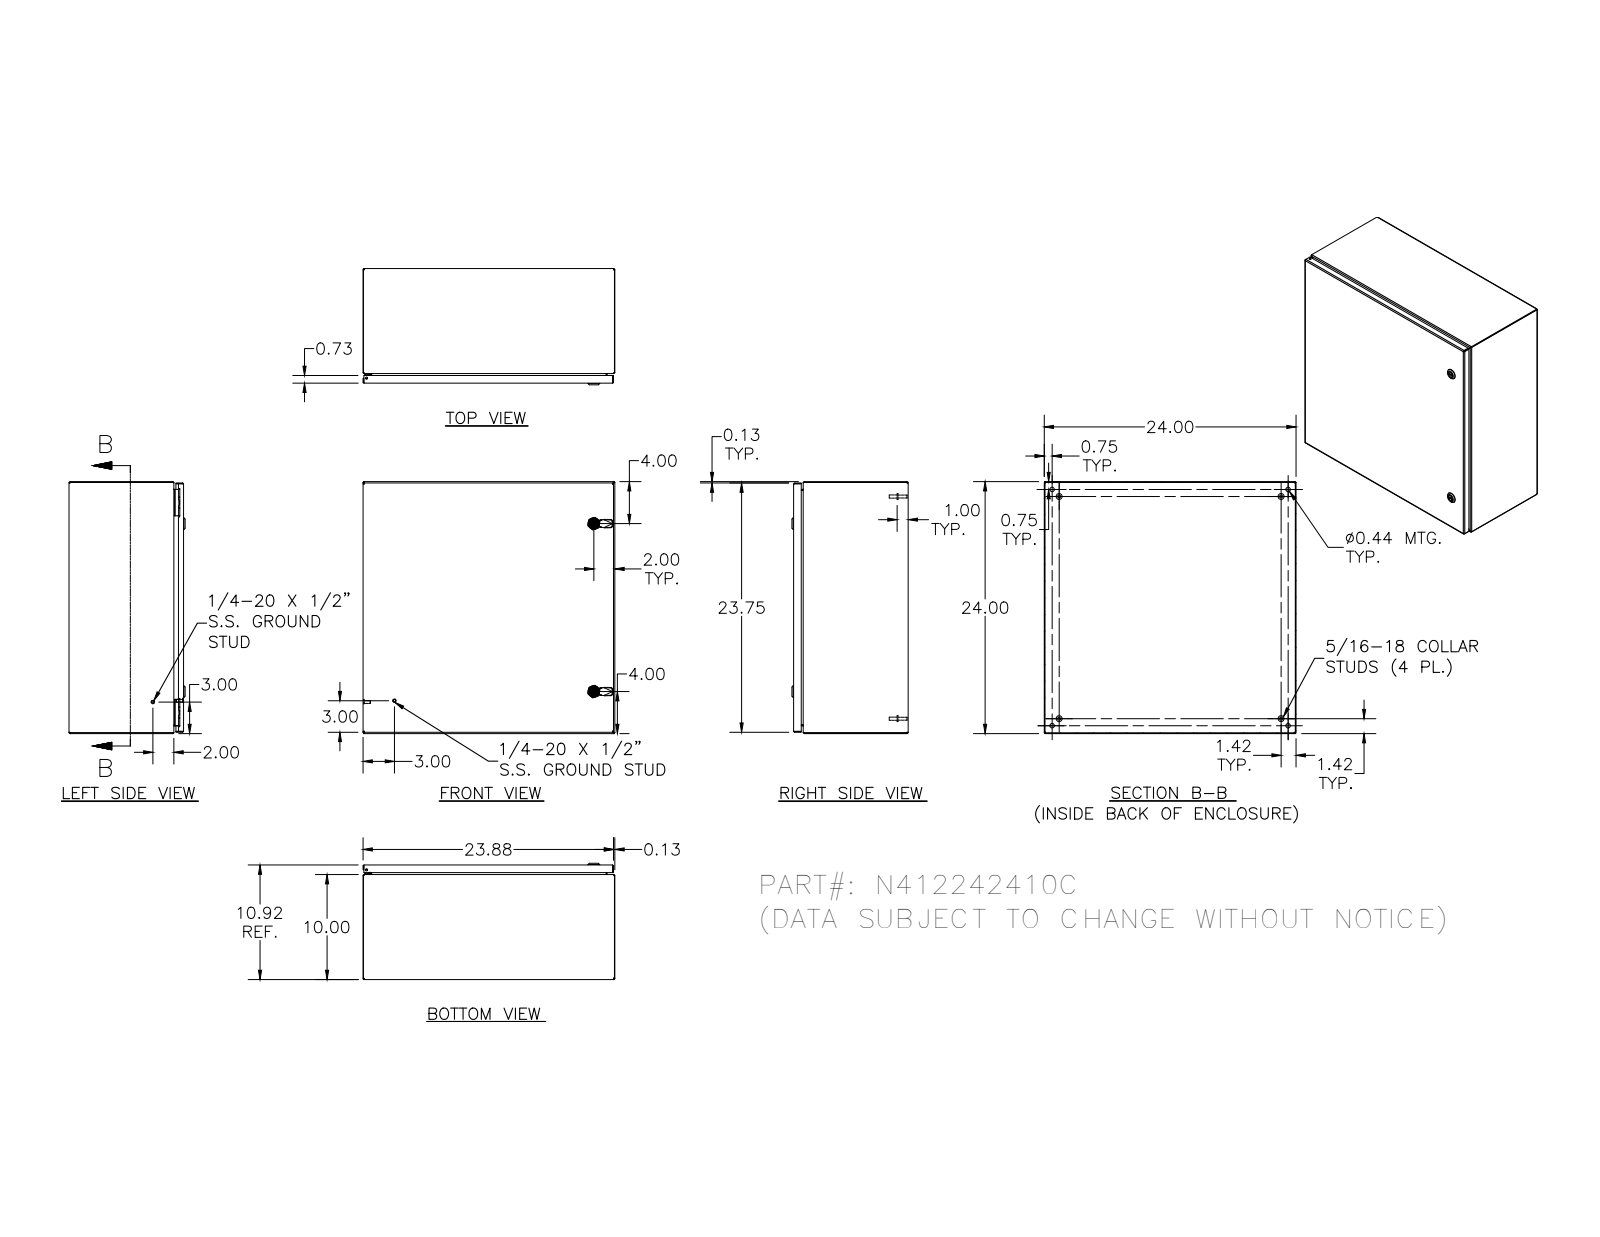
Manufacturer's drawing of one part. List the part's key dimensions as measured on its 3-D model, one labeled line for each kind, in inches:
Part name (STEP PRODUCT): N412242410C
STEP written by: SolidWorks 2018 (AUTOMOTIVE_DESIGN)
Units: inches
Bodies: 40 solids, 1812 faces (704 planar, 676 cylindrical, 432 other)
Overall size (bounding box): 24 × 24 × 11.075
Volume: 171.1 in³ · Surface area: 4 642 in²
Round holes (diameter × count): ⌀0.188 ×5, ⌀0.093 ×4, ⌀0.152 ×4, ⌀0.167 ×4, ⌀0.172 ×4, ⌀0.437 ×4, ⌀0.156 ×2, ⌀0.197 ×2, ⌀0.315 ×2, ⌀0.394 ×2, ⌀0.402 ×2, ⌀0.634 ×2
Round bosses / shafts (diameter × count): ⌀0.25 ×10, ⌀0.563 ×4, ⌀0.36 ×4, ⌀0.32 ×4, ⌀0.3 ×4, ⌀0.256 ×4, ⌀0.164 ×4, ⌀0.131 ×4
Partial cylindrical surfaces — rounded edges, fillets, slot ends (radius × count): R0.012 ×54, R0.031 ×30, R0.05 ×26, R0.02 ×23, R0.105 ×20, R0.016 ×18, R0.125 ×16, R0.032 ×8
Main face-to-face distances: 0.074, 10.843, 10.769, 10.917, 0.074, 23.926, 23.926, 23.852, 24, 0.917
Hole centre spacings: 20, 0.66, 0.656, 1.307, 1.965, 19.34, 20.66, 22.5
